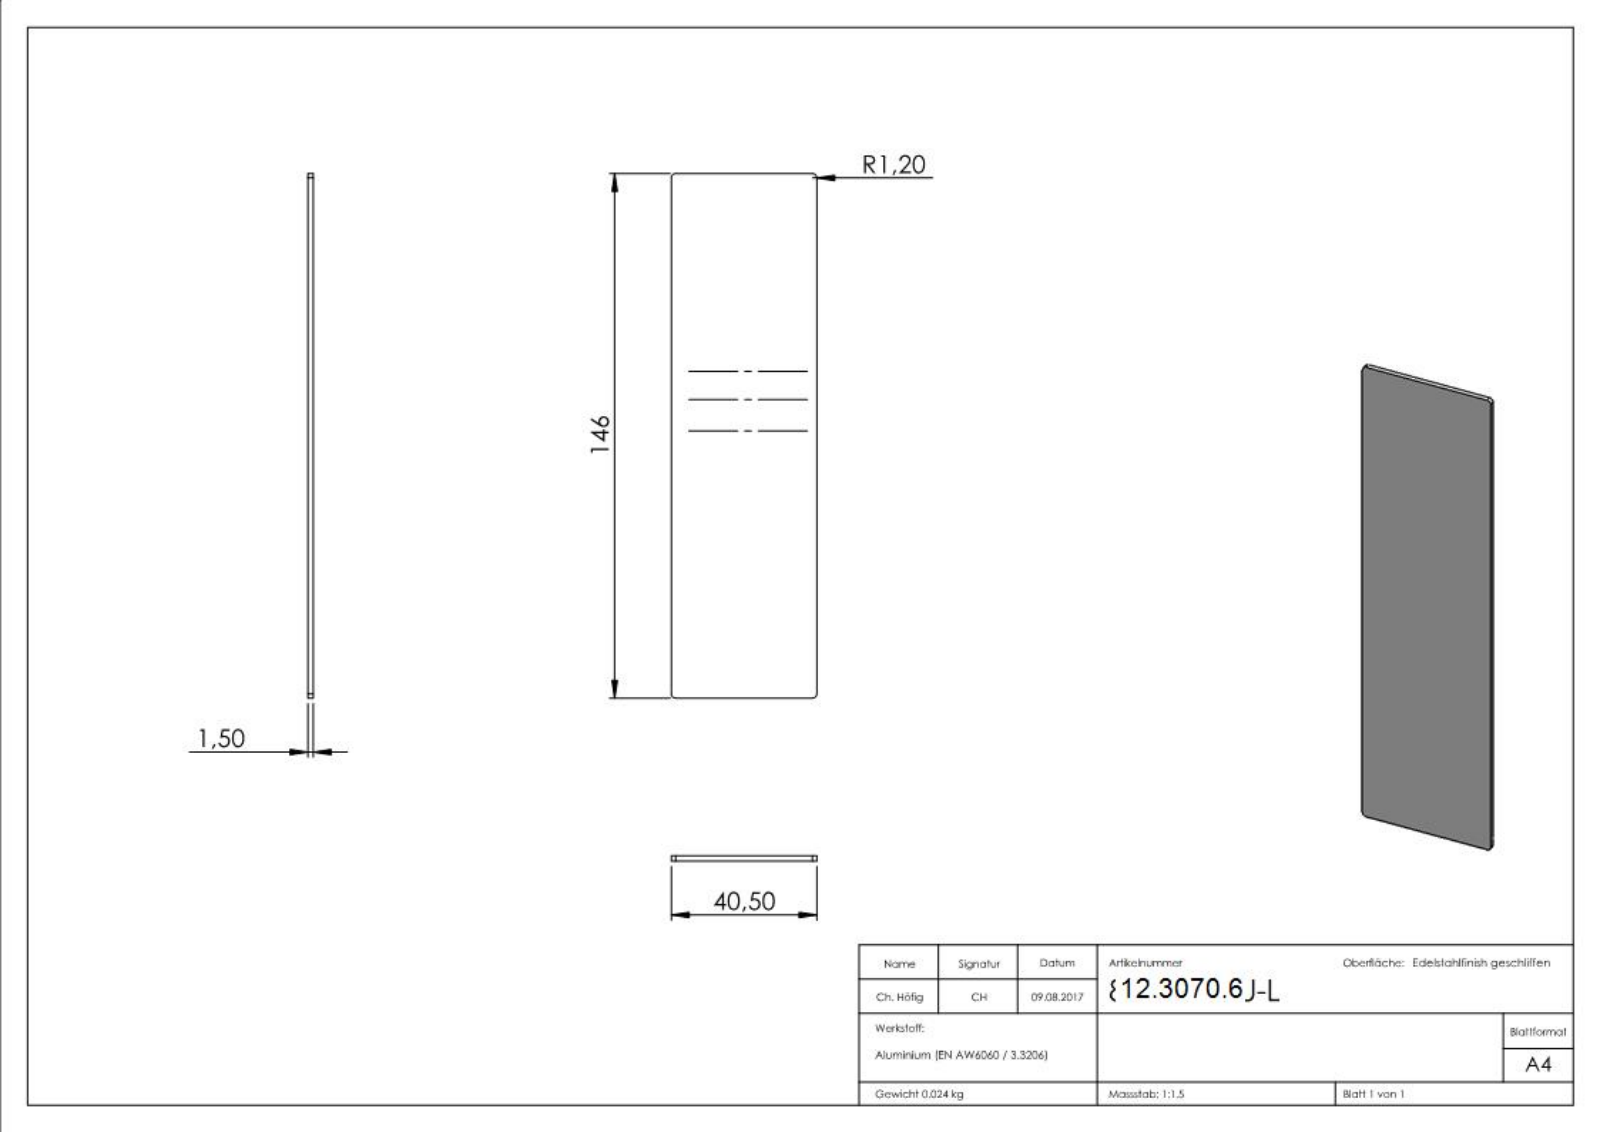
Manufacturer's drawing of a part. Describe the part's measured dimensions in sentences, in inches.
The part is named "80554-ALU-L". Its 3-D file was written by "SolidWorks 2015 (CONFIG_CONTROL_DESIGN)". It is 1 solid with 250 faces: 149 planar, 4 cylindrical and 97 other. Overall it measures 5.748 by 1.594 by 0.059 inches. Its volume is 0.541 cubic inches and its surface area 19.2 square inches. Partial cylindrical surfaces (rounded edges, fillets, slot ends): 4 of radius 0.047. The main face-to-face distances are 0.059, 1.594, 5.748, 0.055, 0.128, 0.017, 0.104, 0.109, 0.071, 0.35.
